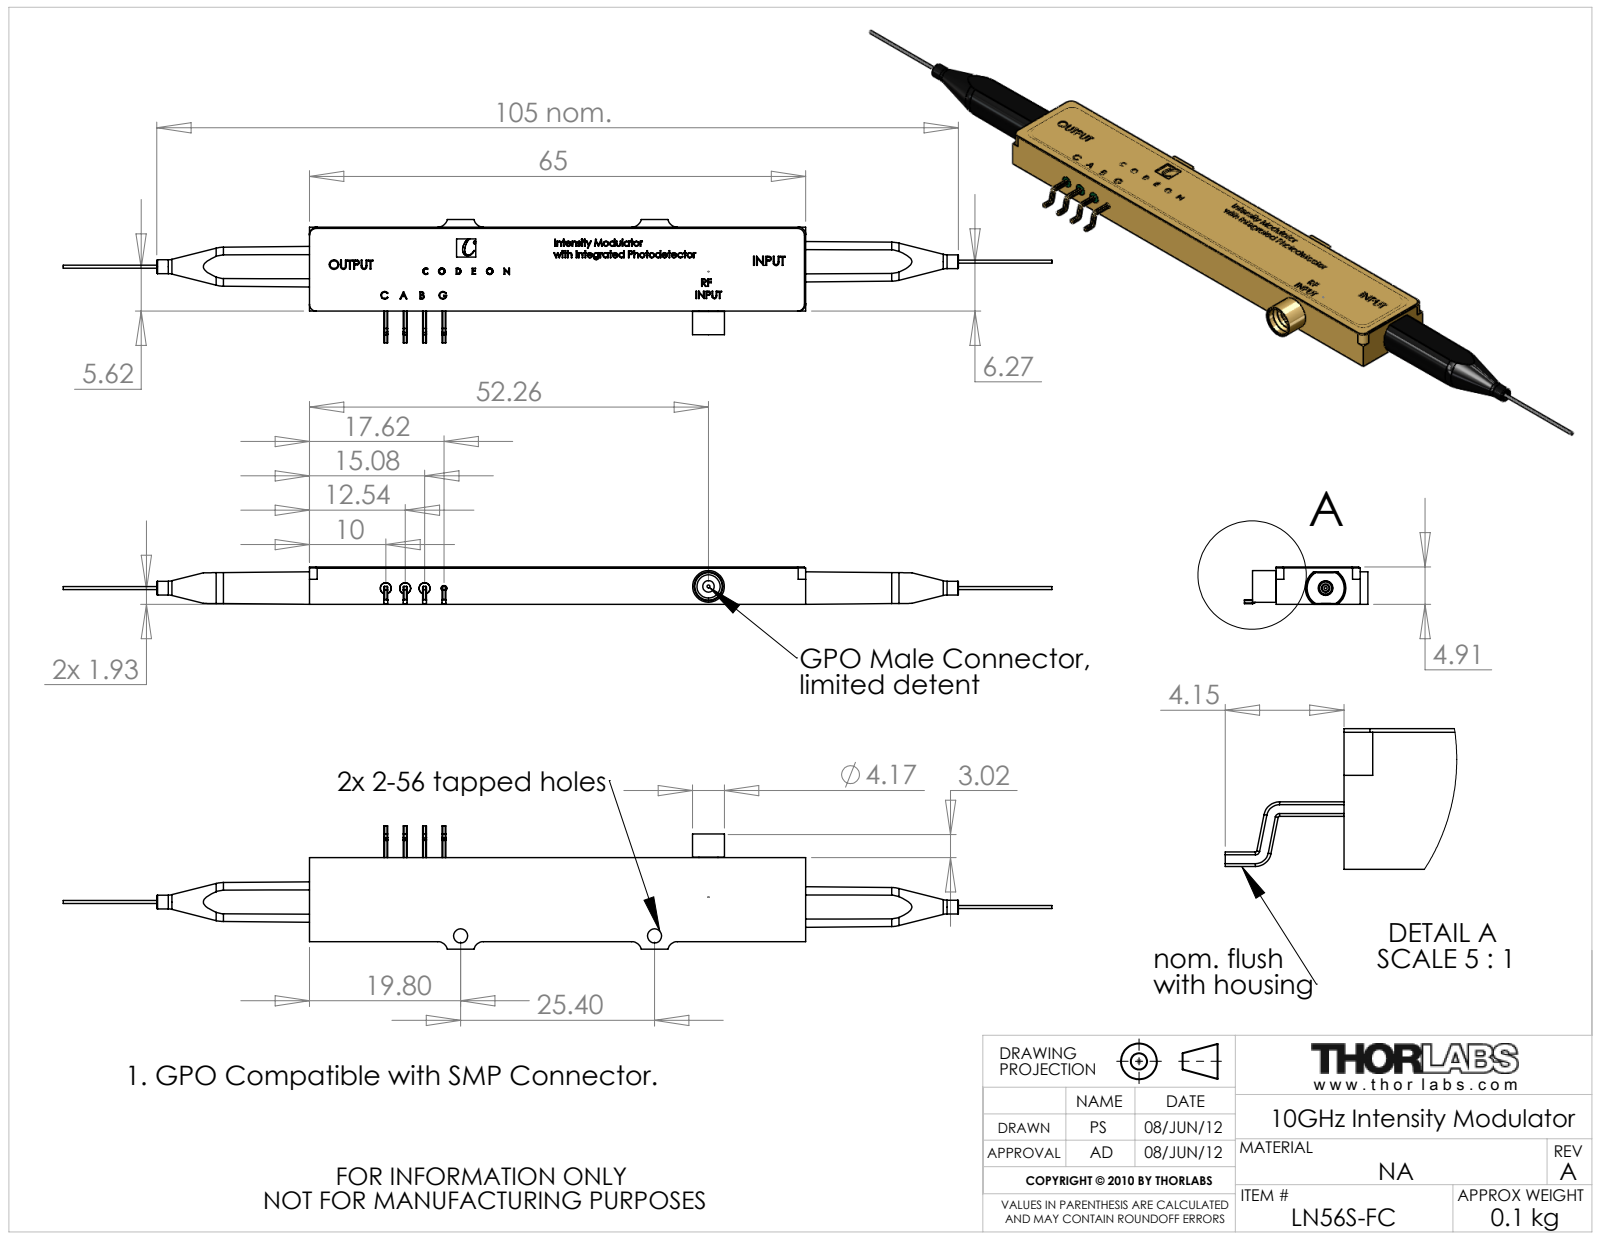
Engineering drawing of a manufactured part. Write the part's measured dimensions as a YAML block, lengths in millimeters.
part_name: "10056-000"
step_written_by: "SolidWorks 2011 (AUTOMOTIVE_DESIGN)"
units: millimeters
bodies: {solids: 0, faces: 771, planar: 464, cylindrical: 100, other: 207}
overall_size: [129.5, 16.15, 4.91]
round_holes:
  - {diameter: 0.5, count: 2}
  - {diameter: 0.9, count: 2}
  - {diameter: 1.85, count: 2}
  - {diameter: 3.05, count: 1}
  - {diameter: 3.17, count: 1}
  - {diameter: 3.61, count: 1}
round_bosses_or_shafts:
  - {diameter: 1.8, count: 2}
  - {diameter: 0.4, count: 2}
  - {diameter: 4.17, count: 1}
partial_cylinders:
  - {radius: 0.1, count: 48}
  - {radius: 0.9, count: 4}
  - {radius: 1, count: 4}
  - {radius: 1.27, count: 4}
  - {radius: 0.55, count: 2}
face_to_face_distances: [4.91, 4.78, 11, 4.84, 65, 12, 1, 2.54, 0.5, 5.08]
hole_center_spacings: [25.4, 0.65, 7.09, 32.47]
